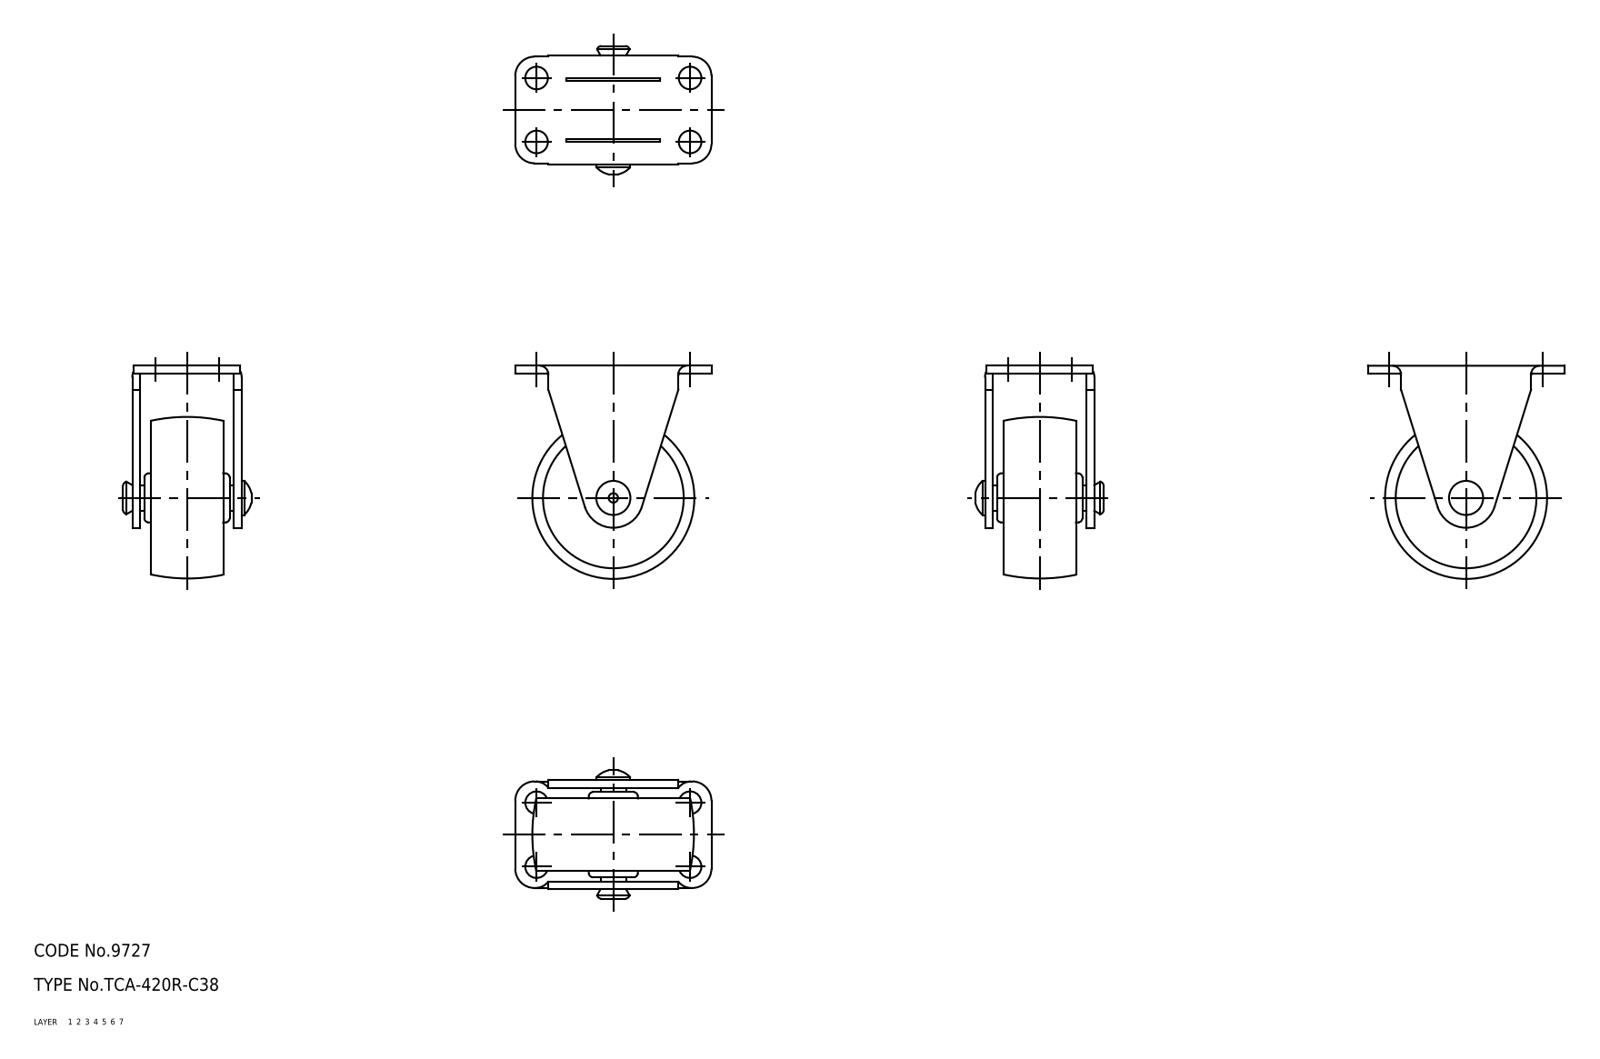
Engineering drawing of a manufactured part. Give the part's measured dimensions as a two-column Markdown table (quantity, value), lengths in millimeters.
| quantity | value |
| --- | --- |
| part name | wheel; axle; No_420_R_C38_3_44_36 |
| STEP written by | CADfix (AUTOMOTIVE_DESIGN) |
| units | millimeters |
| bodies | 3 solids, 116 faces (0 planar, 0 cylindrical, 116 other) |
| overall size | 50 × 46 × 30.1 |
| volume | 20 087 mm³ |
| surface area | 11 369 mm² |
